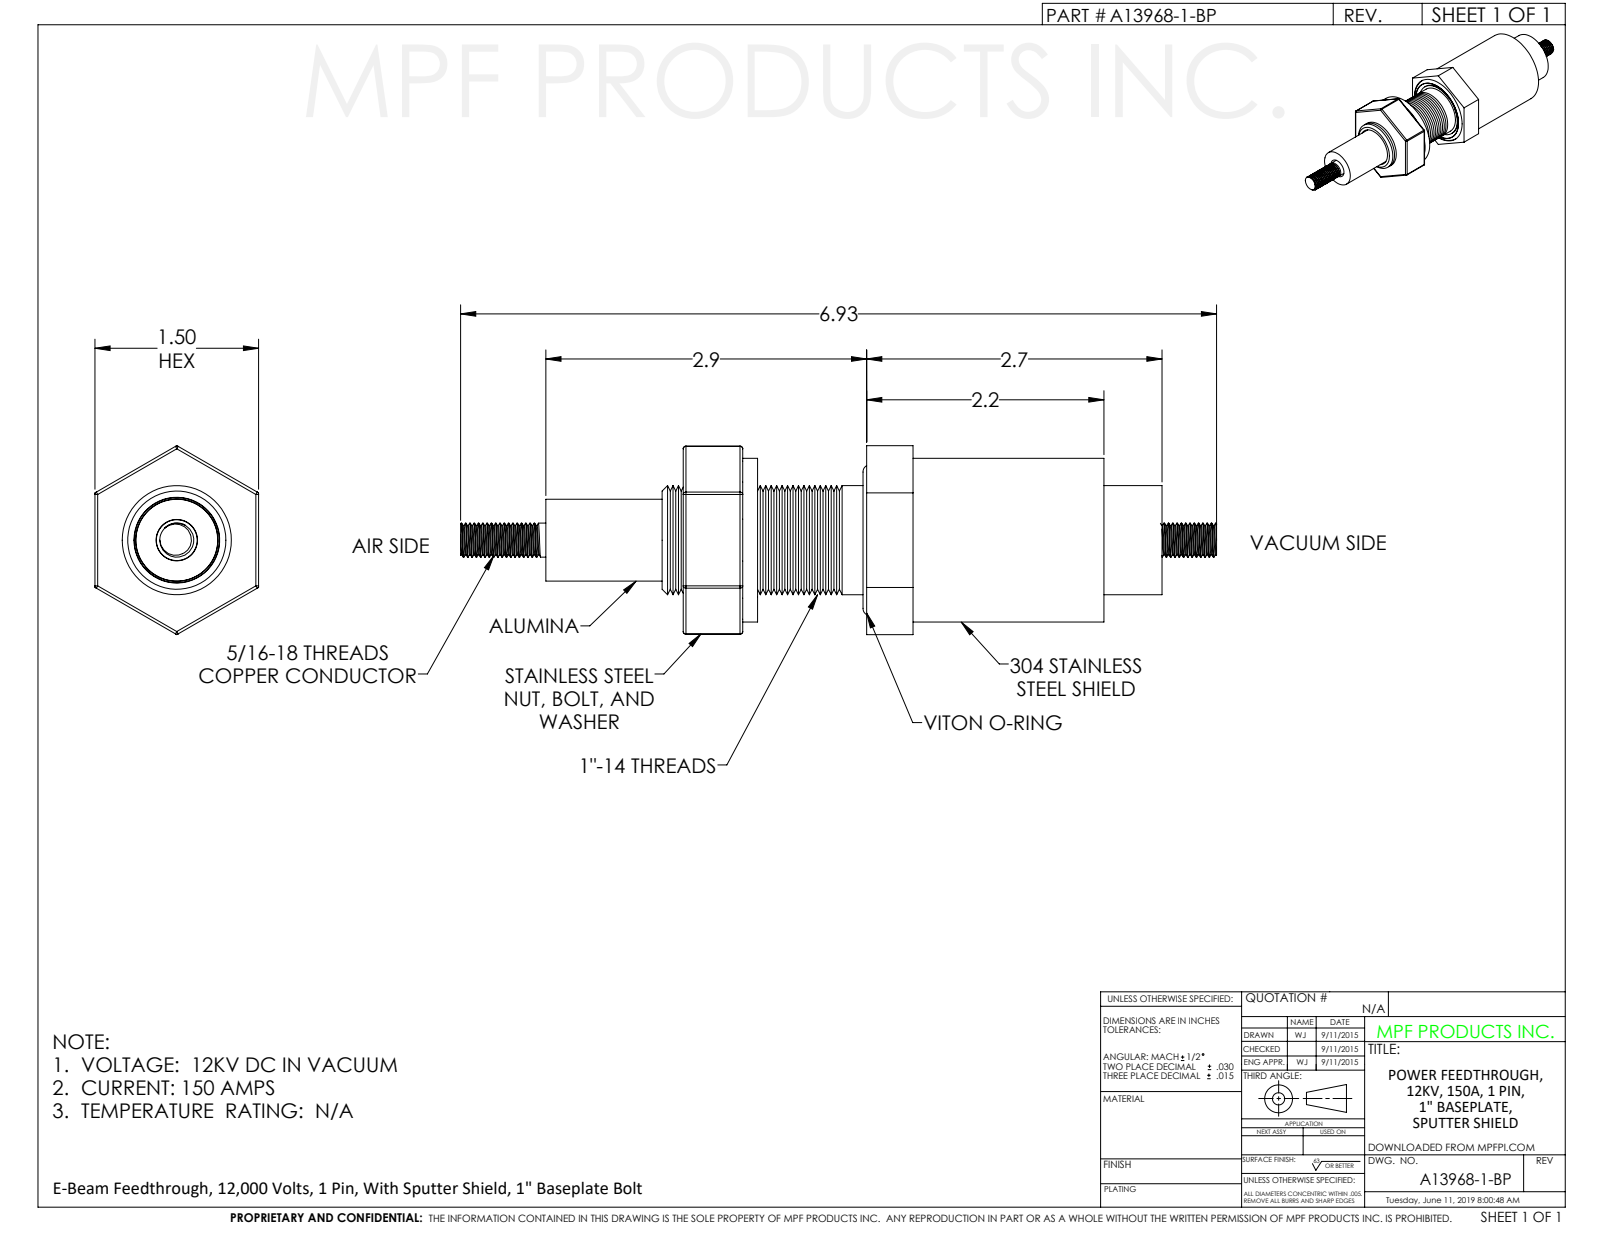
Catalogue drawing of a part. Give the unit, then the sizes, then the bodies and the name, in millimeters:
Units: millimetres
Overall size (bounding box): 176 × 44 × 38.1
Round holes (diameter × count): ⌀26.3 ×1, ⌀33.1 ×1, ⌀34.8 ×1, ⌀35.3 ×1
Round bosses / shafts (diameter × count): ⌀38.1 ×1, ⌀34.7 ×1, ⌀28.2 ×1, ⌀25.4 ×1, ⌀19.1 ×1, ⌀7.9 ×1
Partial cylindrical surfaces — rounded edges, fillets, slot ends (radius × count): R0.6 ×18
Main face-to-face distances: 38.1, 36.2, 53.5, 17.3, 25.4, 68.8, 58, 94.2, 111.5, 10.8
Volume: 87 670 mm³ · Surface area: 34 430 mm²
Bodies: 1 solid, 349 faces (49 planar, 108 cylindrical, 192 other)
Part name (STEP PRODUCT): A13968-1
STEP written by: SolidWorks 2019 (CONFIG_CONTROL_DESIGN)
